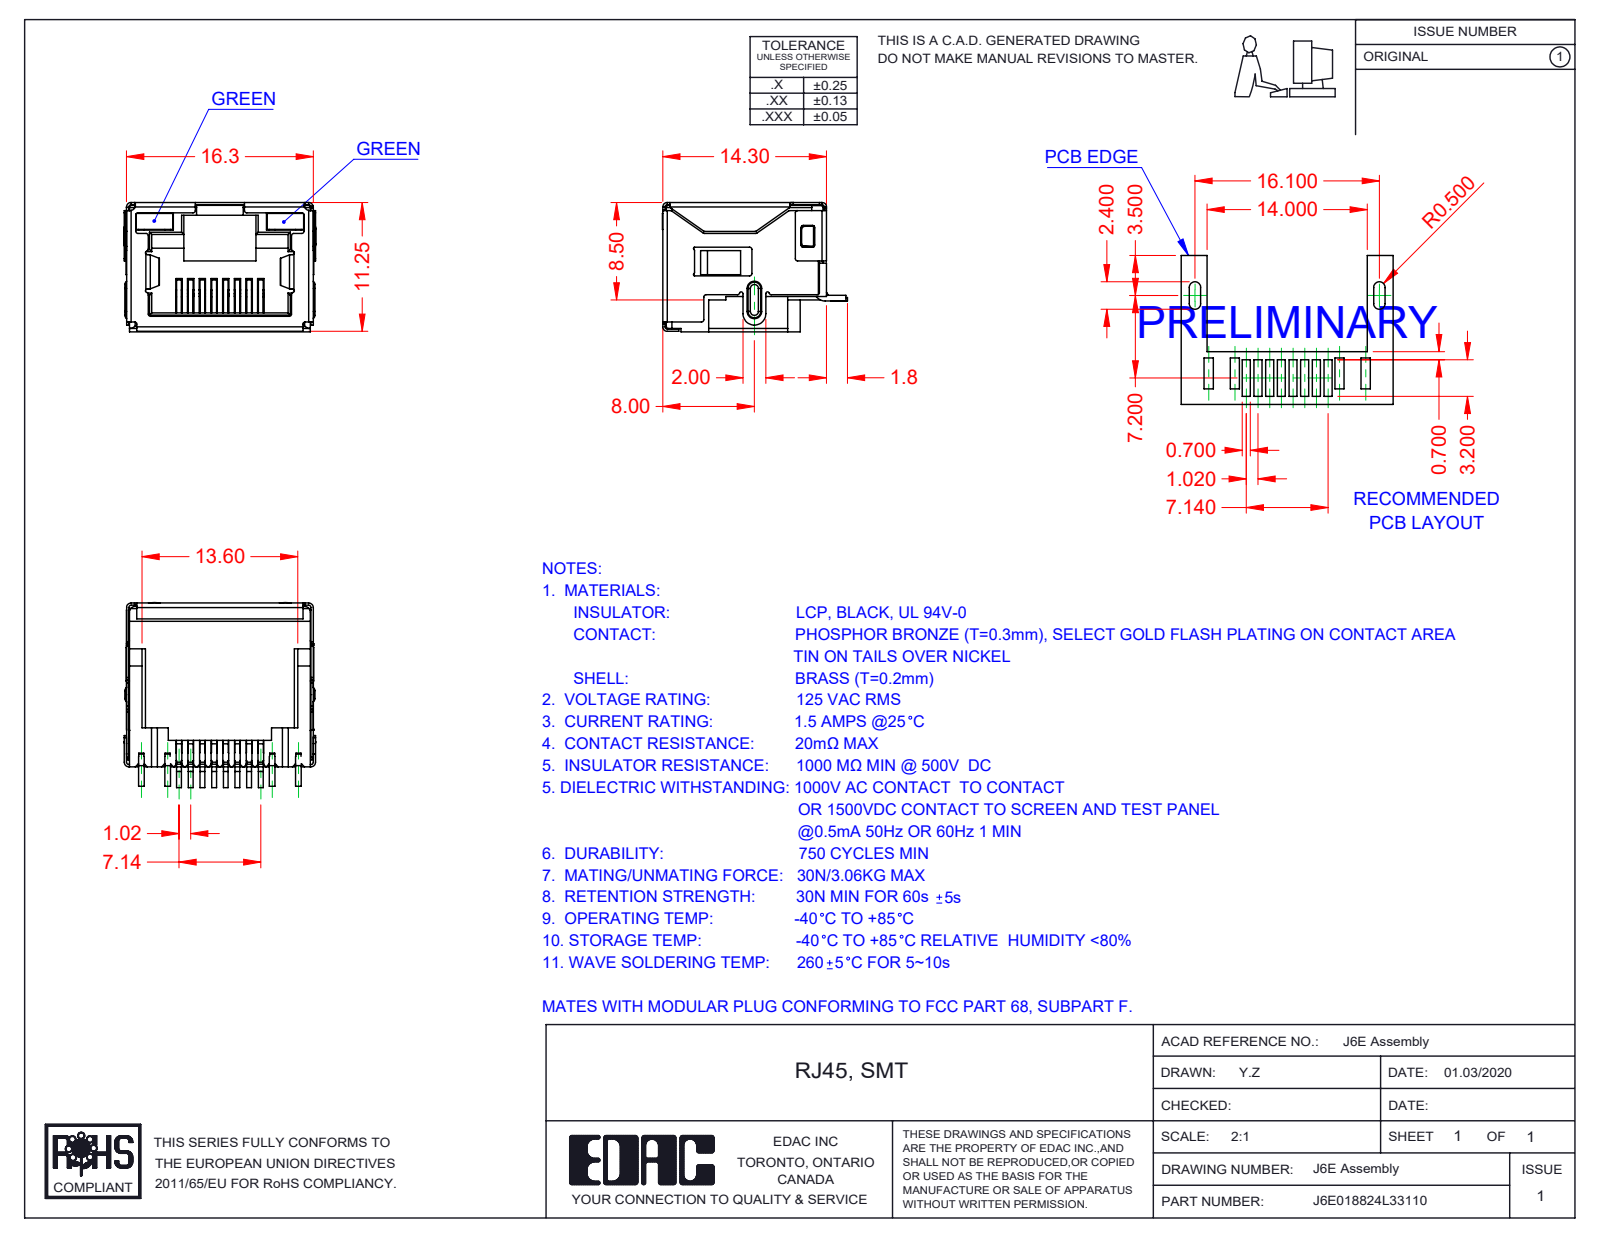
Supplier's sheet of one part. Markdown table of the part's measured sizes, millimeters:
| quantity | value |
| --- | --- |
| part name | 6E Contacts; 6E Insulator_LED; 6E LED RH_3-Green; 6E LED LH_3-Green (+2 more) |
| STEP written by | SolidWorks 2016 (CONFIG_CONTROL_DESIGN) |
| units | millimeters |
| bodies | 12 solids, 1496 faces (1099 planar, 347 cylindrical, 50 other) |
| overall size | 16.75 × 16.15 × 11.3 |
| volume | 1 109 mm³ |
| surface area | 4 045 mm² |
| partial cylindrical surfaces (radius × count) | 0.2 × 82, 0.25 × 17, 0.4 × 13, 0.5 × 13, 0.1 × 10, 0.15 × 7, 0.3 × 4, 1 × 3 |
| main face-to-face distances | 11.05, 16.05, 16.1, 15.85, 11.1, 11.3, 2.4, 0.7, 9.85, 0.49 |
